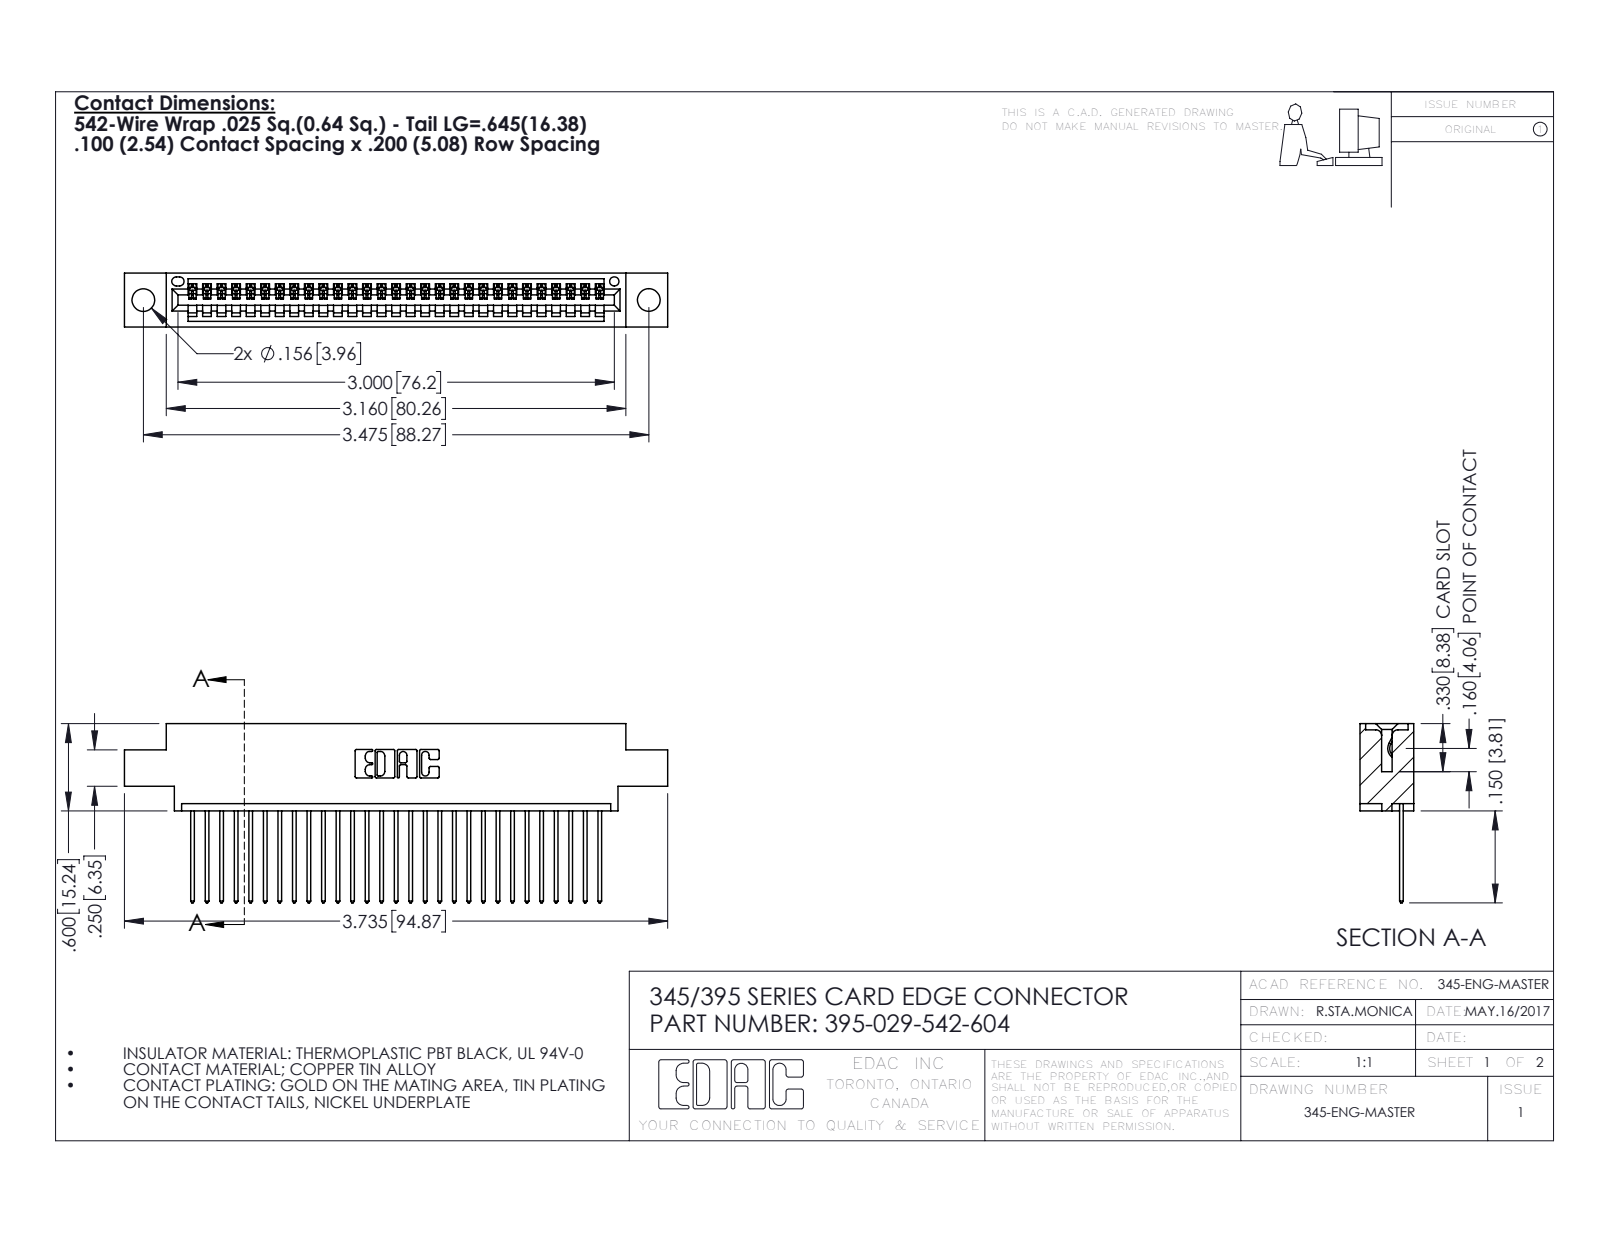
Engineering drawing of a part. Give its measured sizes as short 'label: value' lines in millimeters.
name: 395-029-542-604; 345-292-001_345-293-142; 345 Part_0.170 Offset - 0.156 Dia-TH
written by: SolidWorks 2016 (CONFIG_CONTROL_DESIGN)
unit: mm
bodies: 30 solids, 1812 faces (1244 planar, 568 cylindrical, 0 other)
size: 94.9 × 31.3 × 9.4
volume: 8 770 mm³; area: 11 820 mm²
holes: 2× ⌀4, 1× ⌀1.6
rounds: 58× R0.2, 58× R0.3, 22× R0.3, 6× R0.2, 6× R0.8, 3× R0.7, 2× R0.8, 2× R1
face distances: 7.6, 1.8, 9.4, 2.5, 6.9, 0.6, 5.1, 5.7, 4.4, 3.8
hole spacings: 6.9, 82.3, 88.3
